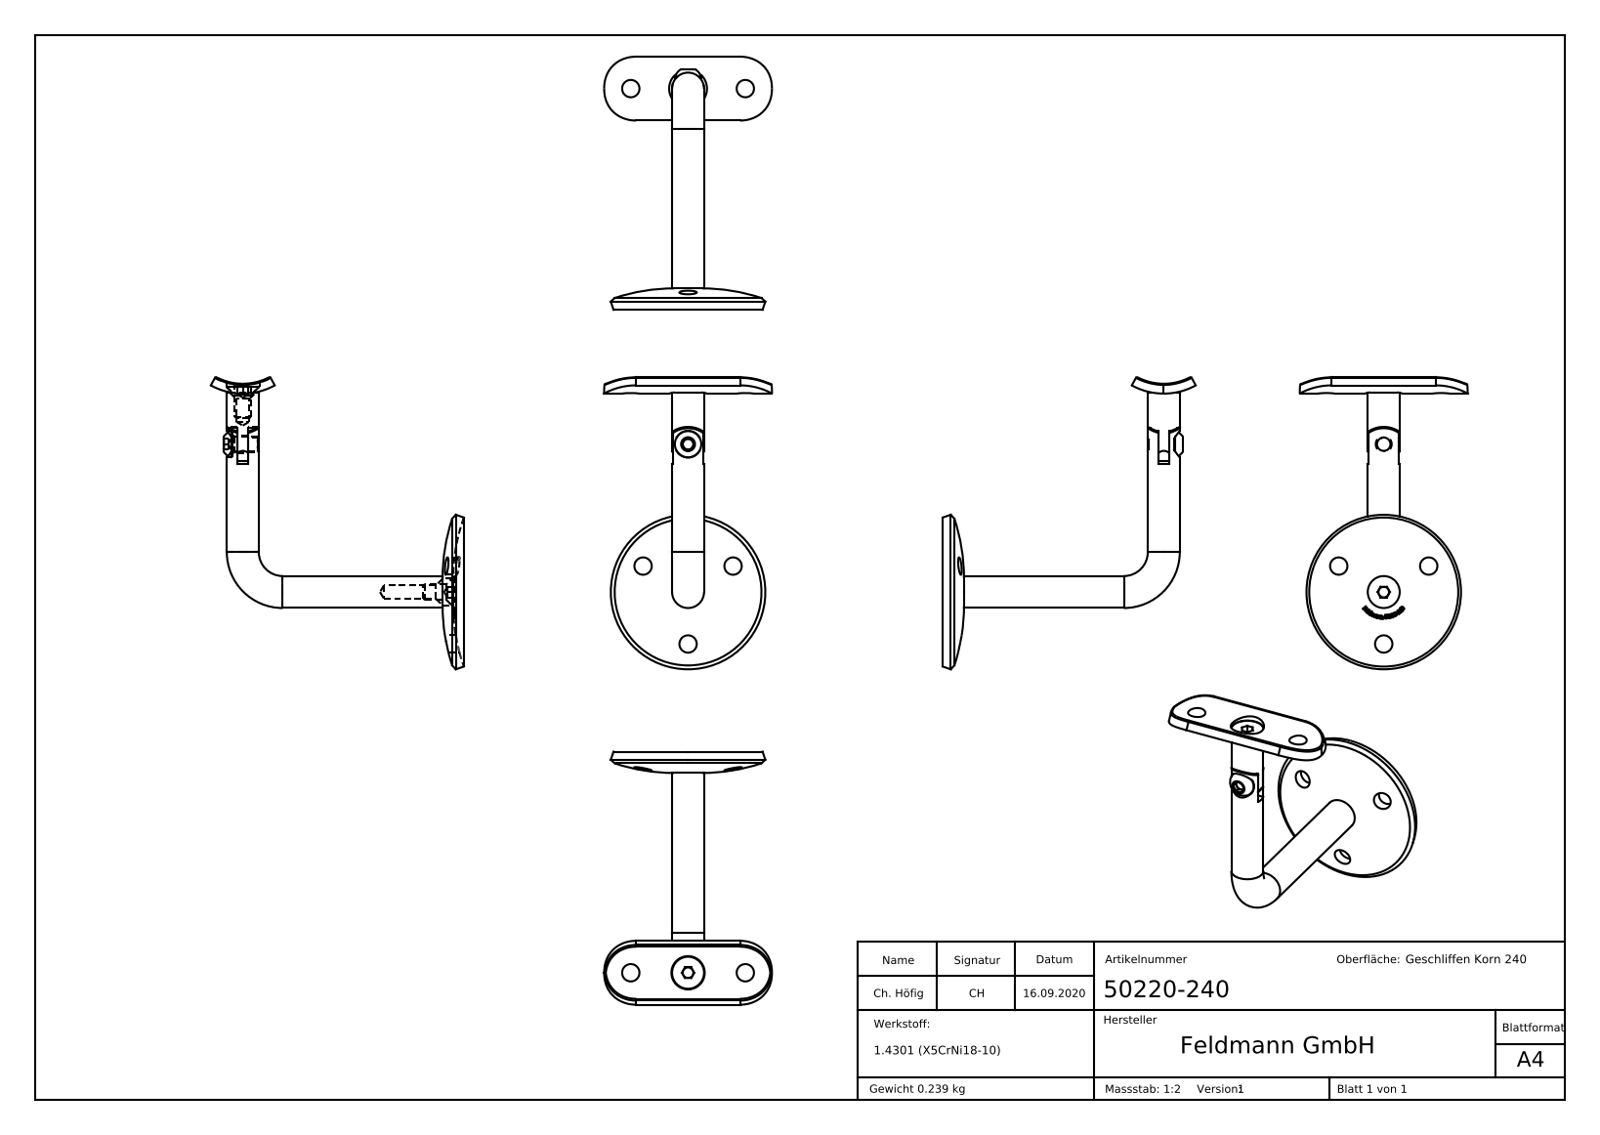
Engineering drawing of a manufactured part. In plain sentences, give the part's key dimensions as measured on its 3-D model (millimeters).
The part is named "50220-240 Teil2; 50220-240 Teil1; 50220-240 Teil4; 50220-240 Teil4_60182-240 (+8 more)". Its 3-D file was written by "SolidWorks 2018 (CONFIG_CONTROL_DESIGN)". It is 7 solids with 382 faces: 144 planar, 60 cylindrical and 178 other. Overall it measures 12003.2 by 6000 by 6000 millimeters. Its volume is 30 201 cubic millimeters and its surface area 17 378 square millimeters. Round holes: 6 of diameter 6.5, 3 of diameter 5, 1 of diameter 5.5, 1 of diameter 10.5, 1 of diameter 12.5. Round bosses or shafts: 3 of diameter 6, 2 of diameter 12, 1 of diameter 9.9. Partial cylindrical surfaces (rounded edges, fillets, slot ends): 4 of radius 12, 2 of radius 0.5, 1 of radius 5, 1 of radius 6.5, 1 of radius 7.1, 1 of radius 10, 1 of radius 10.5, 1 of radius 21.2. The main face-to-face distances are 4, 3.95, 2.2, 77.8, 81.8, 77.85, 81.75, 3.9, 83.8, 6. The hole center spacings are 19.5, 33.78, 21.5, 48.77, 43, 55.5, 75.
